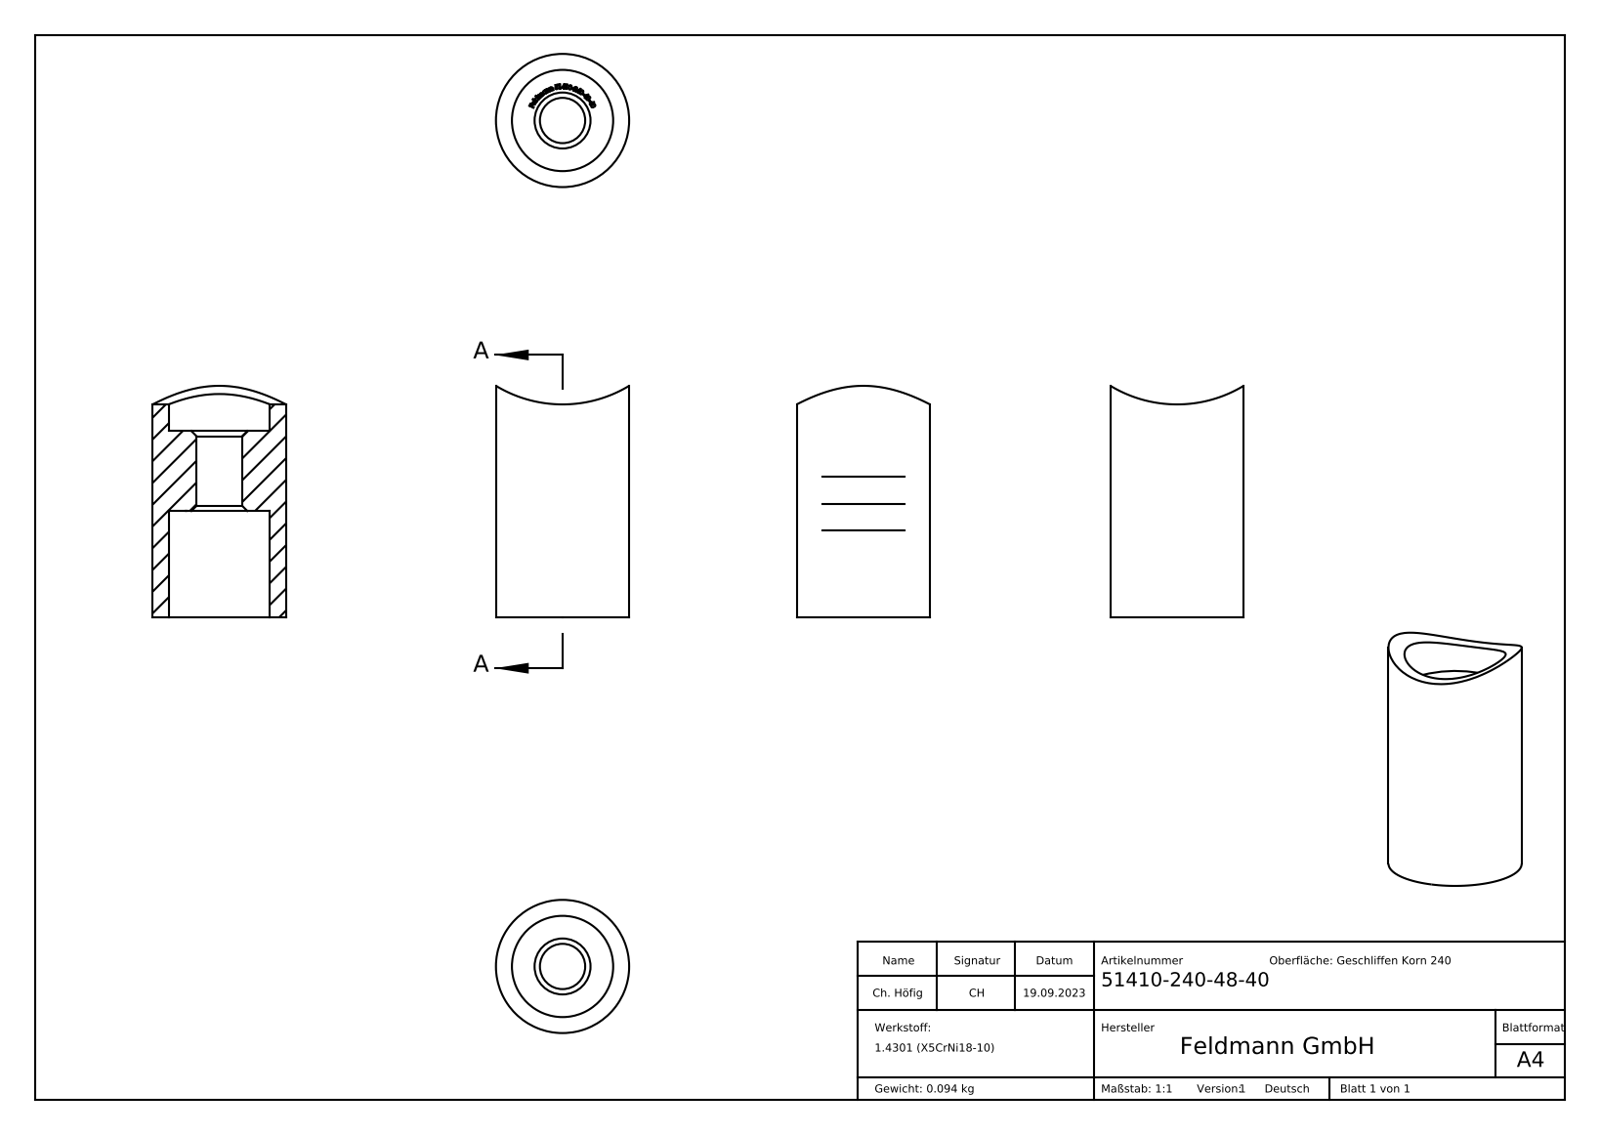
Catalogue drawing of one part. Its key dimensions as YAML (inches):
part_name: "51410-240-48-40"
step_written_by: "SolidWorks 2018 (CONFIG_CONTROL_DESIGN)"
units: inches
bodies: {solids: 1, faces: 293, planar: 180, cylindrical: 5, other: 108}
overall_size: [1.712, 0.984, 0.984]
volume: 0.729
surface_area: 9.433
round_holes:
  - {diameter: 0.335, count: 1}
  - {diameter: 0.748, count: 1}
round_bosses_or_shafts:
  - {diameter: 0.984, count: 1}
partial_cylinders:
  - {radius: 0.951, count: 1}
face_to_face_distances: [1.378, 0.787, 0.591, 0.791, 0.587, 0.016, 0.017, 0.013, 0.019, 0.014]
